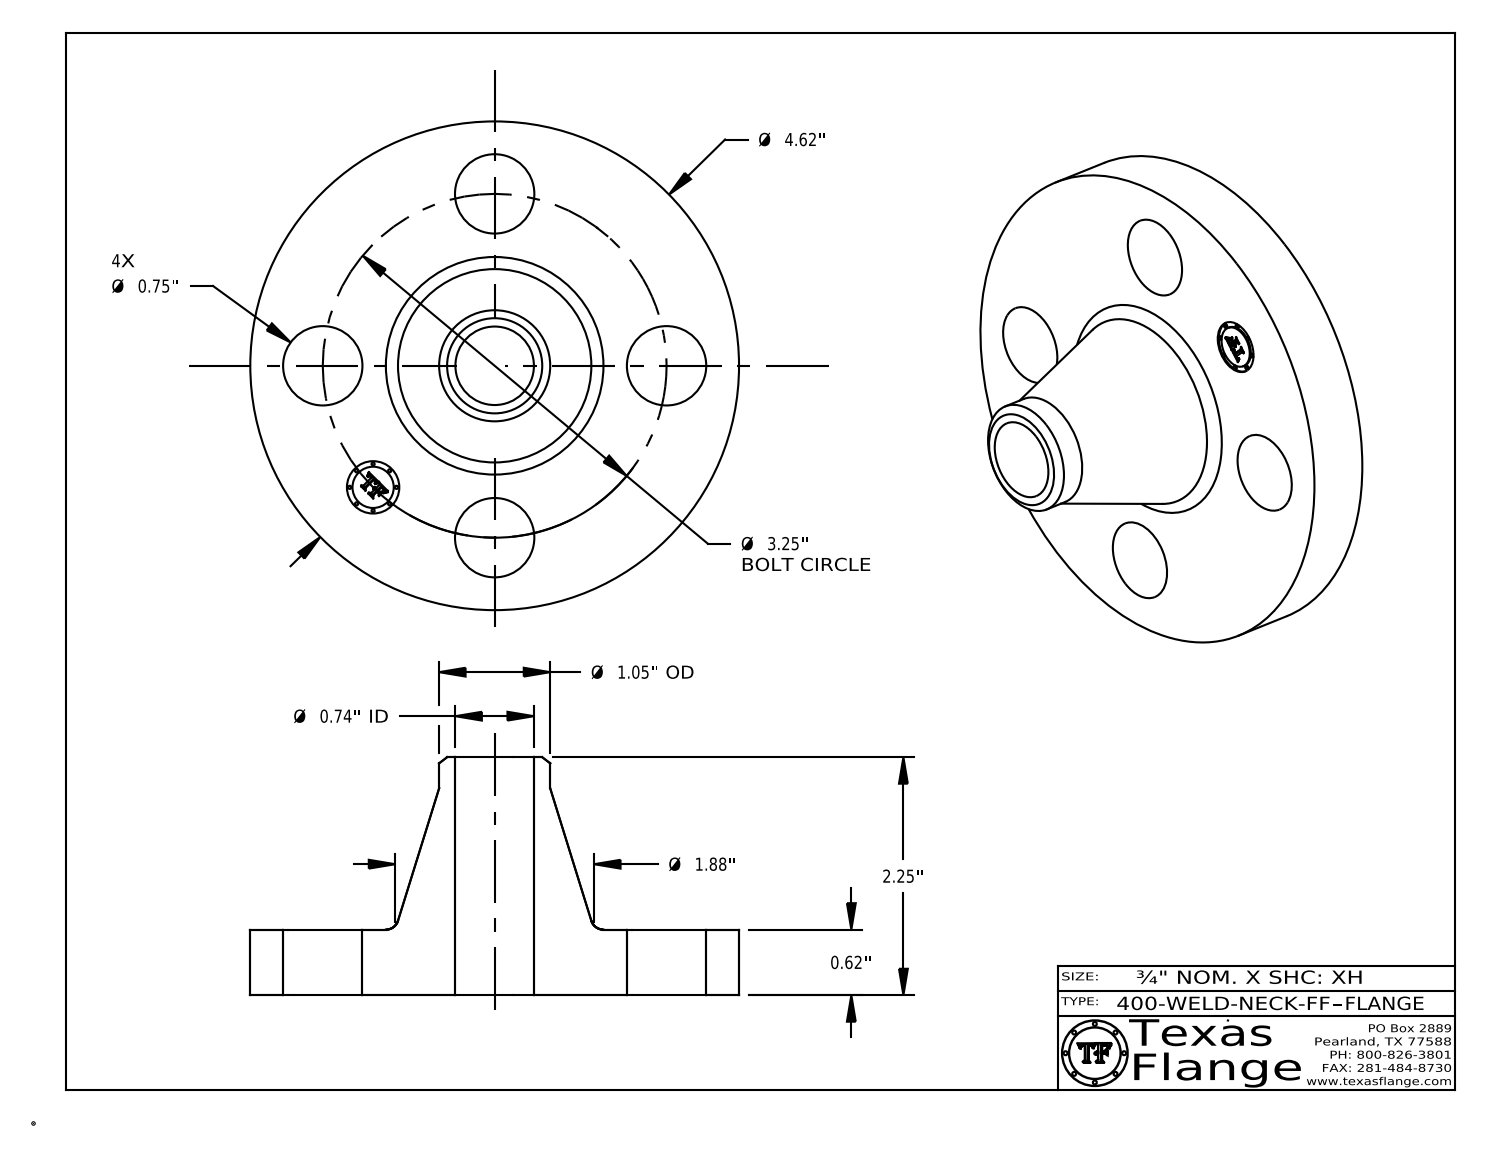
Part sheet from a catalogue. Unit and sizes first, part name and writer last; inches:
Units: inches
Overall size (bounding box): 4.62 × 4.62 × 2.25
Round holes (diameter × count): ⌀0.75 ×4, ⌀0.495 ×1, ⌀0.742 ×1
Round bosses / shafts (diameter × count): ⌀0.03 ×8, ⌀4.62 ×1, ⌀1.05 ×1, ⌀0.39 ×1
Main face-to-face distances: 0.62, 2.25, 1.63, 0.605, 0.015, 1.645, 0.148, 0.144, 0.027, 0.096
Hole centre spacings: 1.625, 2.298, 1.244, 3.003, 3.25
Volume: 10.89 in³ · Surface area: 54.54 in²
Bodies: 1 solid, 408 faces (368 planar, 34 cylindrical, 6 other)
Part name (STEP PRODUCT): 400-WELD-NECK-FF
STEP written by: CATIA V5 STEP AP214 (AUTOMOTIVE_DESIGN)
